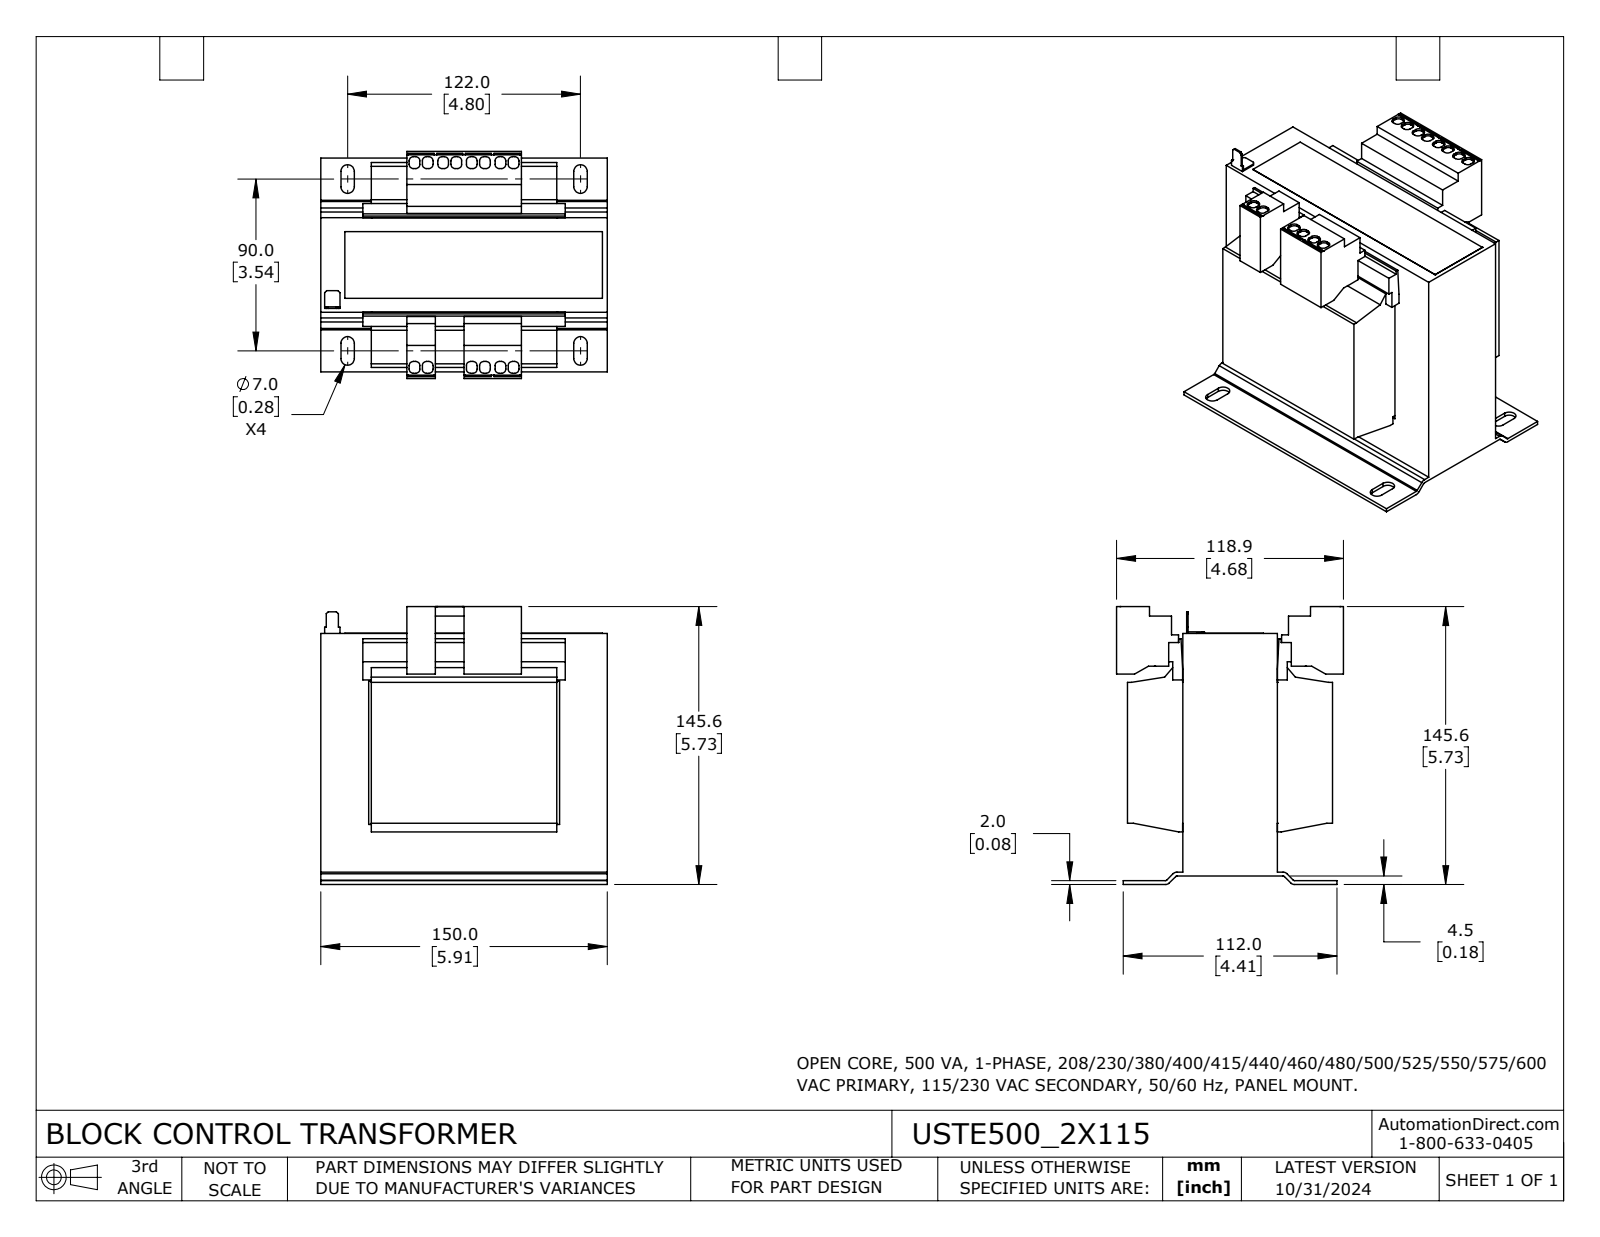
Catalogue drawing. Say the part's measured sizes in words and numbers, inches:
The part is named "USTE500_2X115". Its 3-D file was written by "SolidWorks 2023 (CONFIG_CONTROL_DESIGN)". It is 1 solid with 429 faces: 357 planar, 72 cylindrical and 0 other. Overall it measures 5.906 by 5.731 by 4.681 inches. Its volume is 90.81 cubic inches and its surface area 259.5 square inches. Partial cylindrical surfaces (rounded edges, fillets, slot ends): 56 of radius 0.087, 8 of radius 0.138, 4 of radius 0.039, 4 of radius 0.118. The main face-to-face distances are 1.14, 3.089, 1.039, 4.866, 1.949, 0.984, 0.079, 4.921, 3.827, 0.055.
